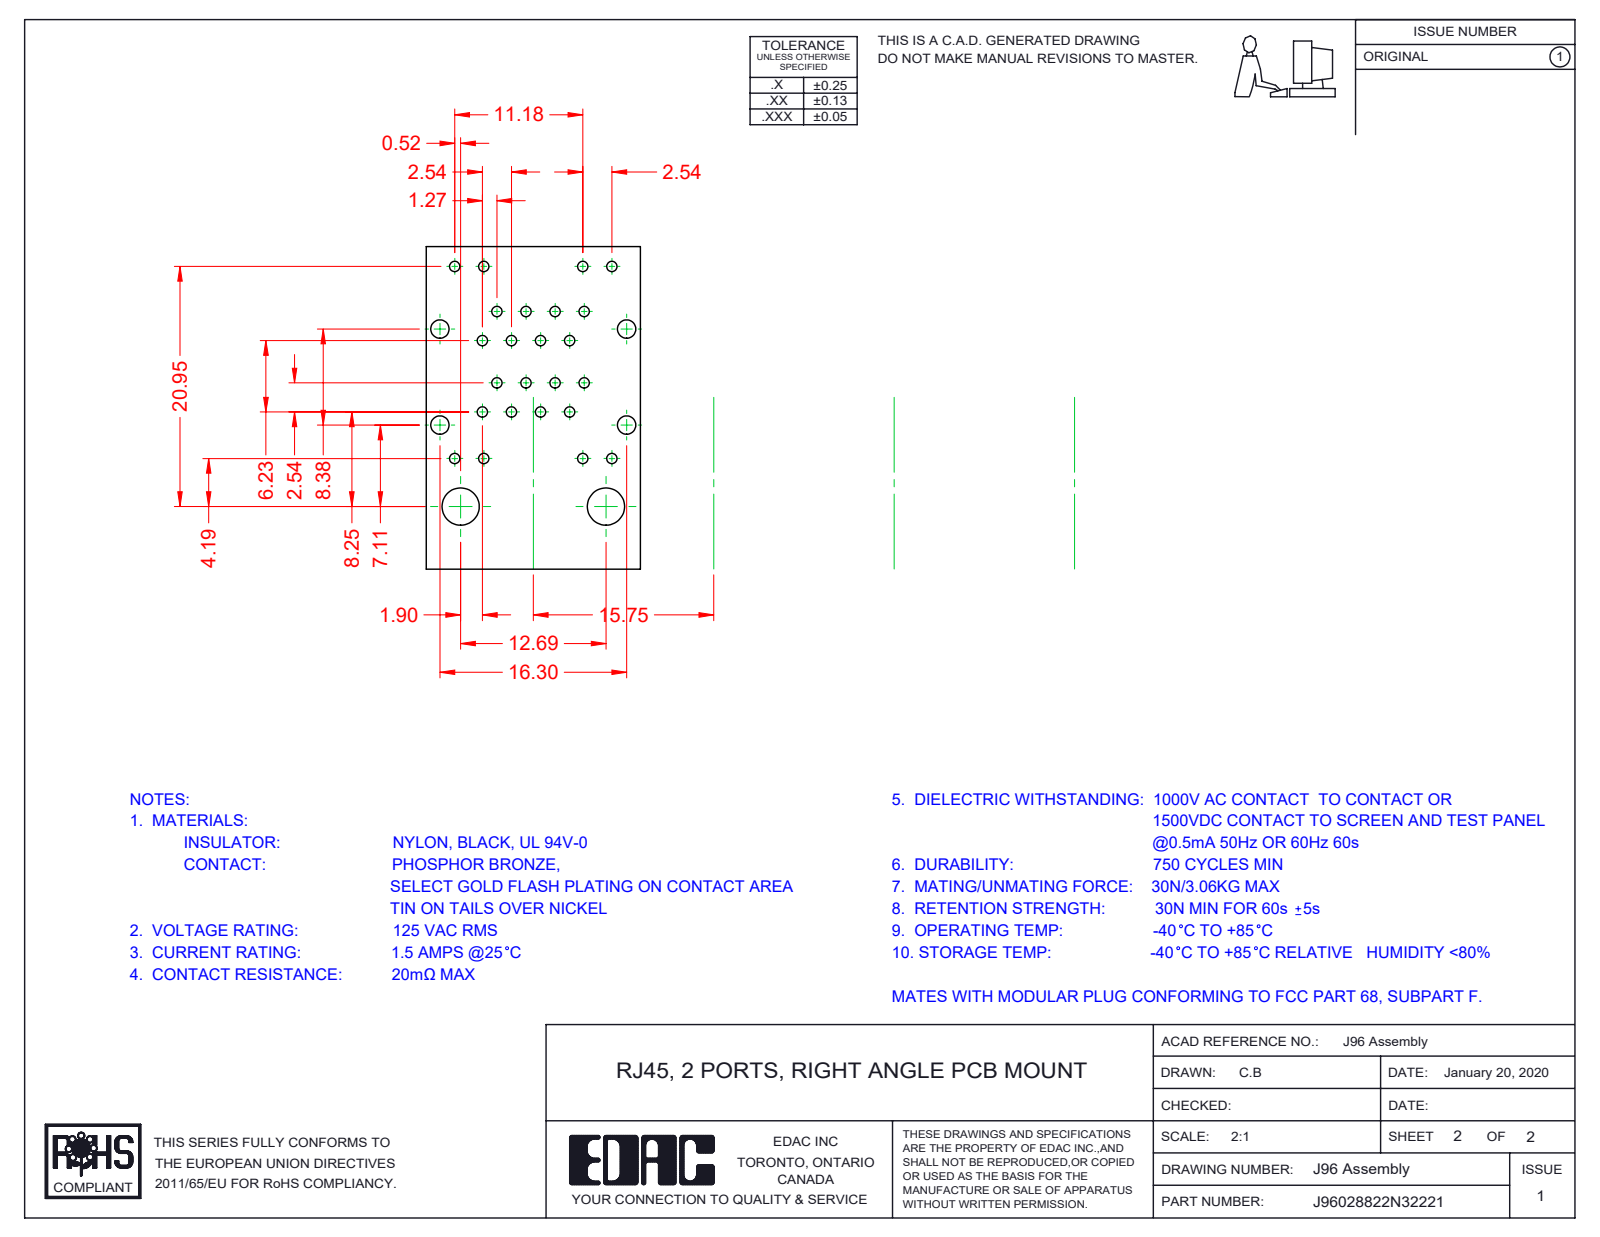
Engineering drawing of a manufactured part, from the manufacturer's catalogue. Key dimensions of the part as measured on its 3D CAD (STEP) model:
Part name (STEP PRODUCT): 96 Grounding_2 Ports; 96 Contact Lock Lower; 96 LED LH Upper_3-Green; 96 Insulator_2 Ports (+8 more)
STEP written by: SolidWorks 2016 (CONFIG_CONTROL_DESIGN)
Units: millimetres
Bodies: 27 solids, 2417 faces (1865 planar, 446 cylindrical, 106 other)
Overall size (bounding box): 31.38 × 28.68 × 16.8
Volume: 6 849 mm³ · Surface area: 19 094 mm²
Partial cylindrical surfaces — rounded edges, fillets, slot ends (radius × count): R0.25 ×48, R0.15 ×32, R0.35 ×24, R0.5 ×16, R1 ×16, R0.2 ×14, R0.7 ×9, R2 ×5
Main face-to-face distances: 16.3, 16.1, 1.75, 16.5, 14.75, 1.55, 14.55, 0.53, 1.48, 11.2
